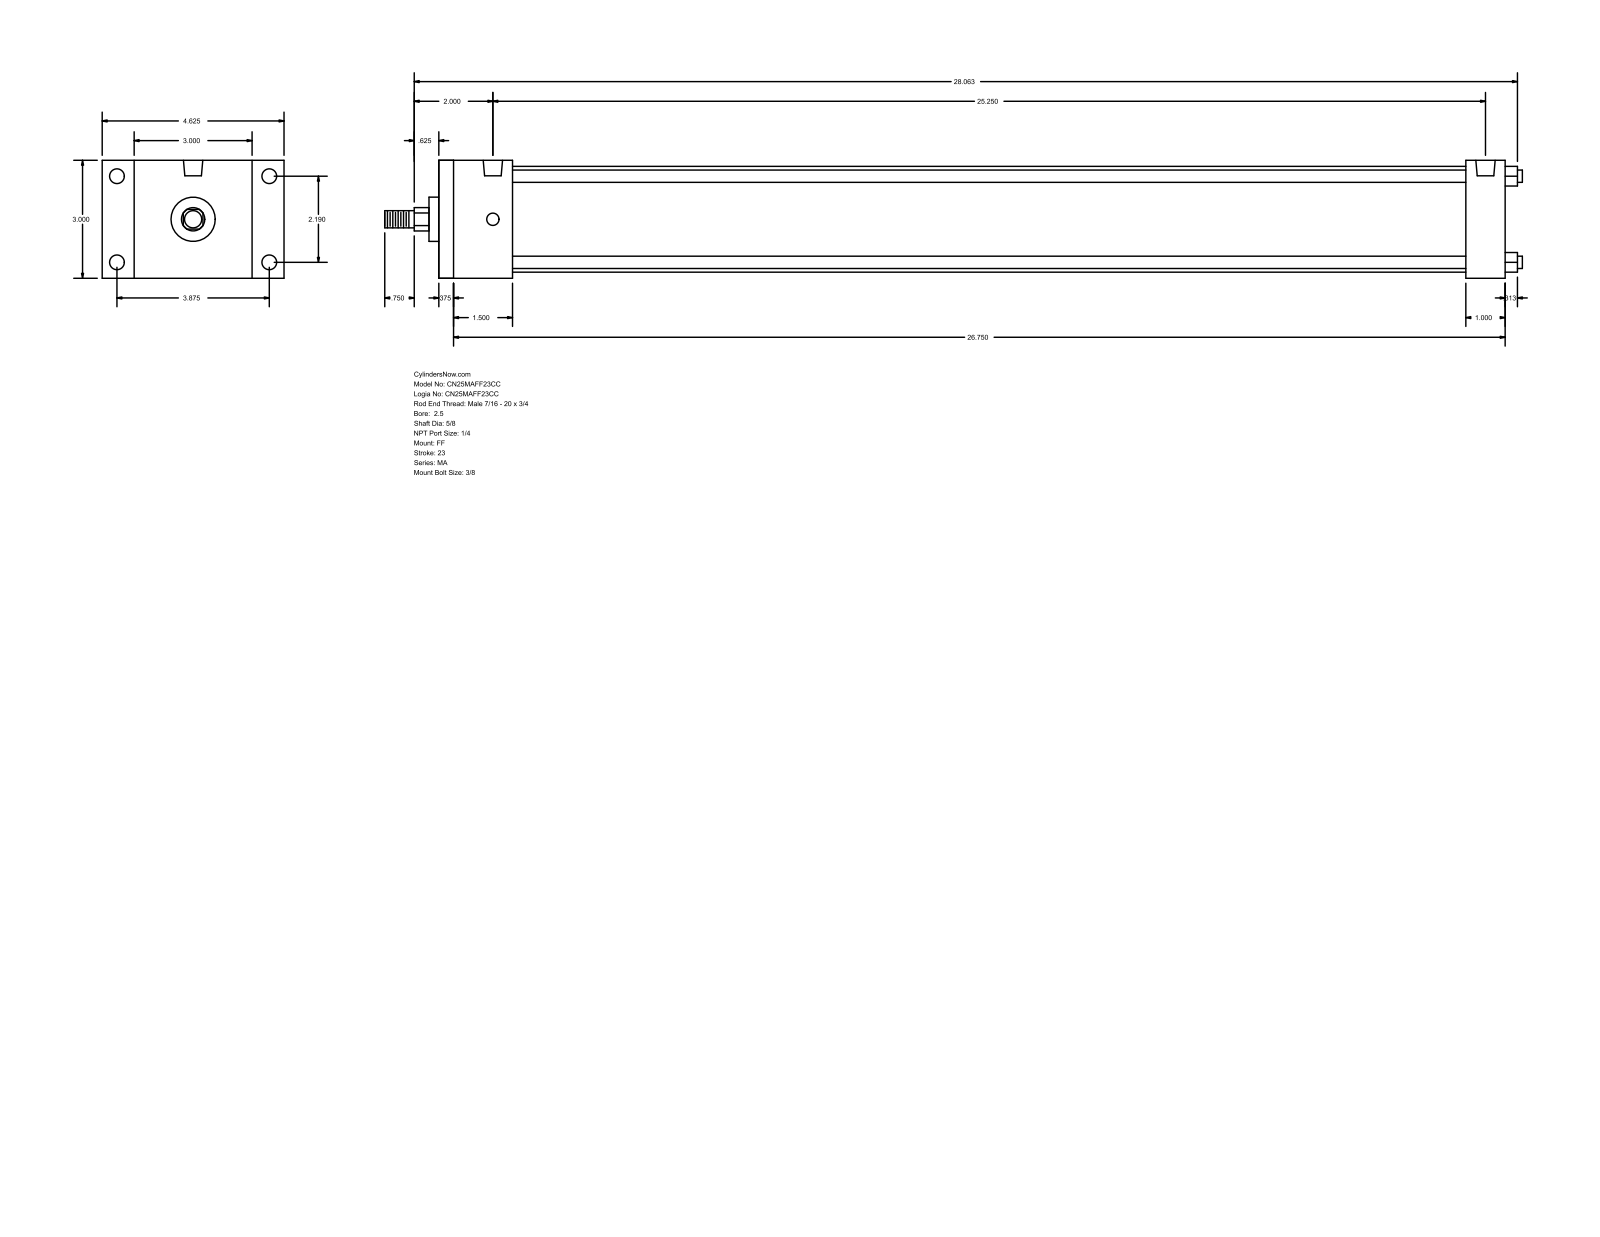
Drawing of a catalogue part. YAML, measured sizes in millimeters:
part_name: "MA_FF__0250_0.625"
step_written_by: "GSSL Pune (CONFIG_CONTROL_DESIGN)"
units: millimeters
bodies: {solids: 0, faces: 92, planar: 64, cylindrical: 28, other: 0}
overall_size: [735.01, 117.47, 76.2]
round_holes:
  - {diameter: 7.94, count: 4}
  - {diameter: 9.53, count: 4}
  - {diameter: 12.49, count: 2}
round_bosses_or_shafts:
  - {diameter: 7.94, count: 4}
  - {diameter: 68.33, count: 1}
  - {diameter: 28.57, count: 1}
  - {diameter: 15.88, count: 1}
  - {diameter: 11.11, count: 1}
partial_cylinders:
  - {radius: 7.54, count: 1}
face_to_face_distances: [76.2, 688.97, 679.45, 9.52, 25.4, 47.62, 663.57, 38.1, 654.05, 615.95]
hole_center_spacings: [55.62, 98.42, 113.05, 641.35]
